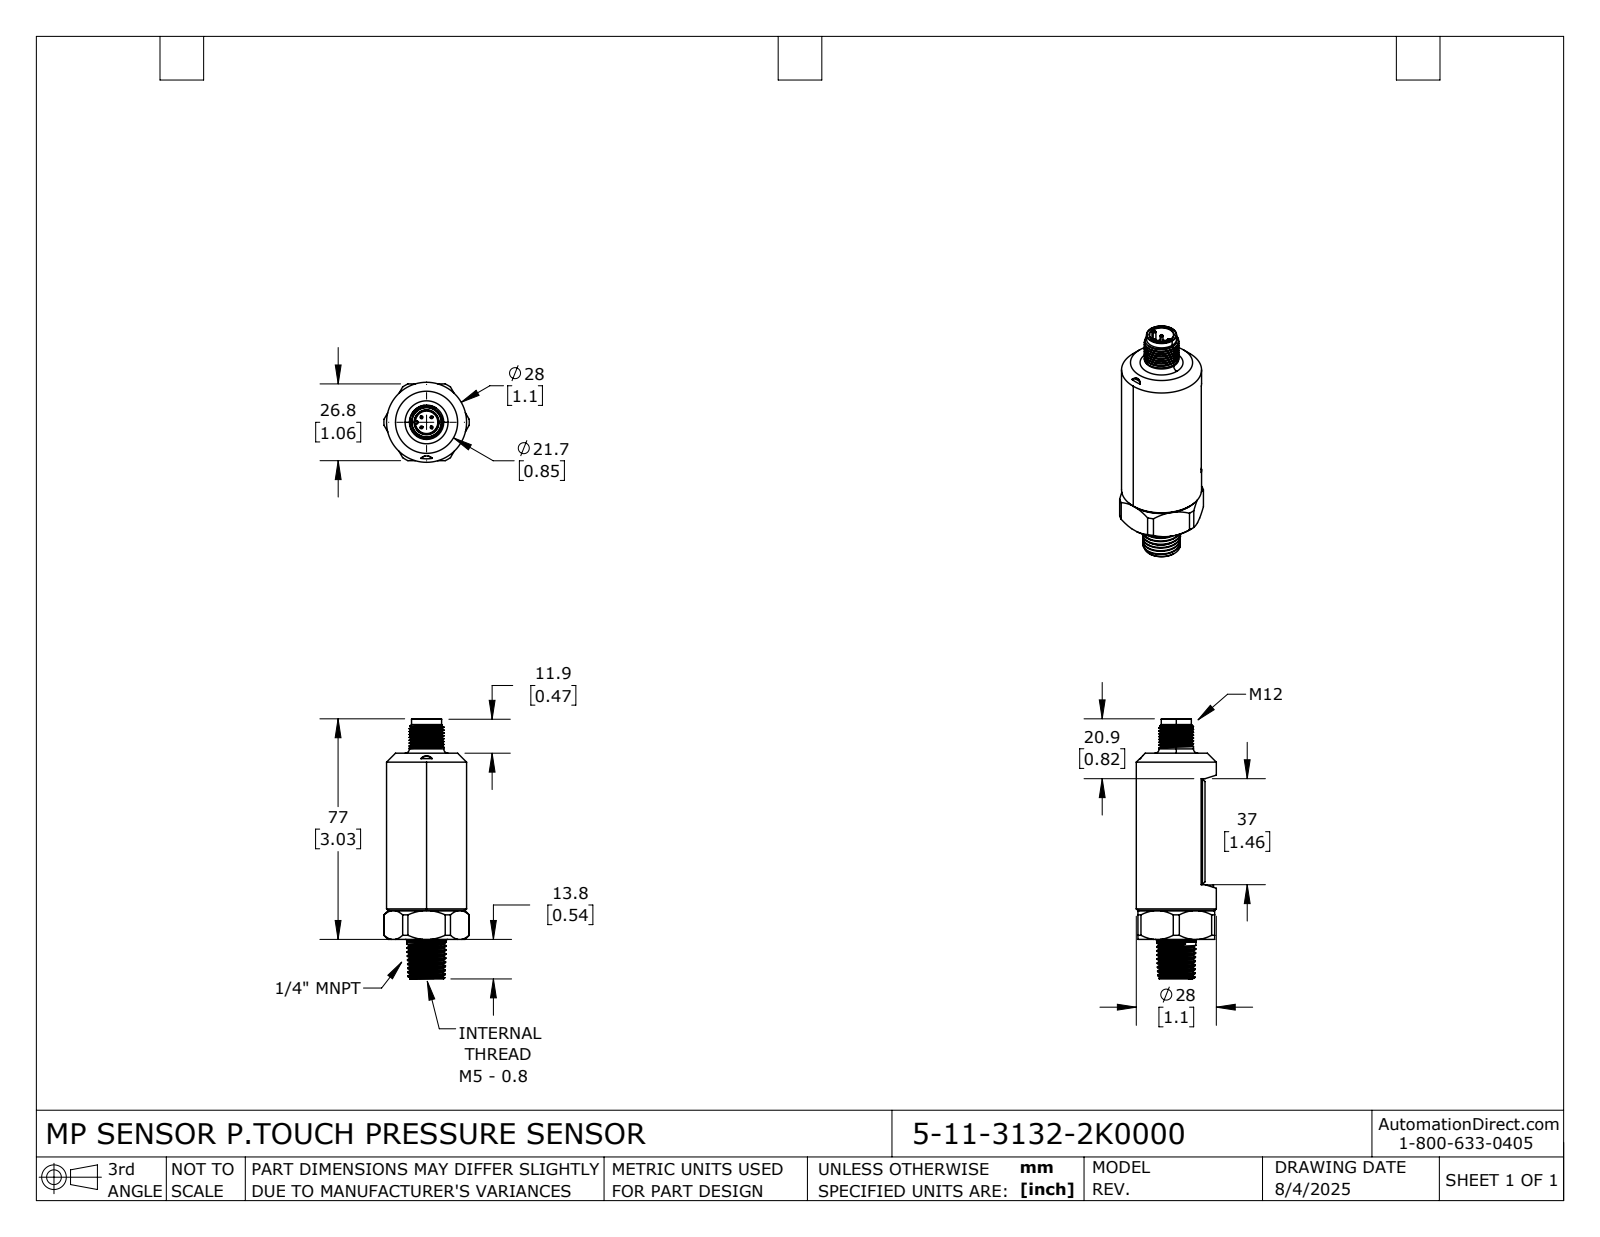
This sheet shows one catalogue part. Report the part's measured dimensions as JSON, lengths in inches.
{"part_name": "5-11-3132-2K0000", "step_written_by": "SolidWorks 2024 (AUTOMOTIVE_DESIGN)", "units": "inches", "bodies": {"solids": 1, "faces": 199, "planar": 46, "cylindrical": 68, "other": 85}, "overall_size": [3.575, 1.173, 1.1], "volume_in3": 2.423, "surface_area_in2": 13.82, "round_holes": [[0.079, 1], [0.165, 1], [0.331, 1]], "round_bosses_or_shafts": [[0.039, 4], [1.1, 1], [1.024, 1], [0.539, 1], [0.472, 1], [0.413, 1]], "partial_cylinders_radius": [[0.006, 2], [0.092, 1], [0.587, 1]], "face_to_face_distances": [1.055, 2.559, 0.922, 0.133, 0.543, 3.102, 0.354, 1.811, 0.35, 0.186]}
